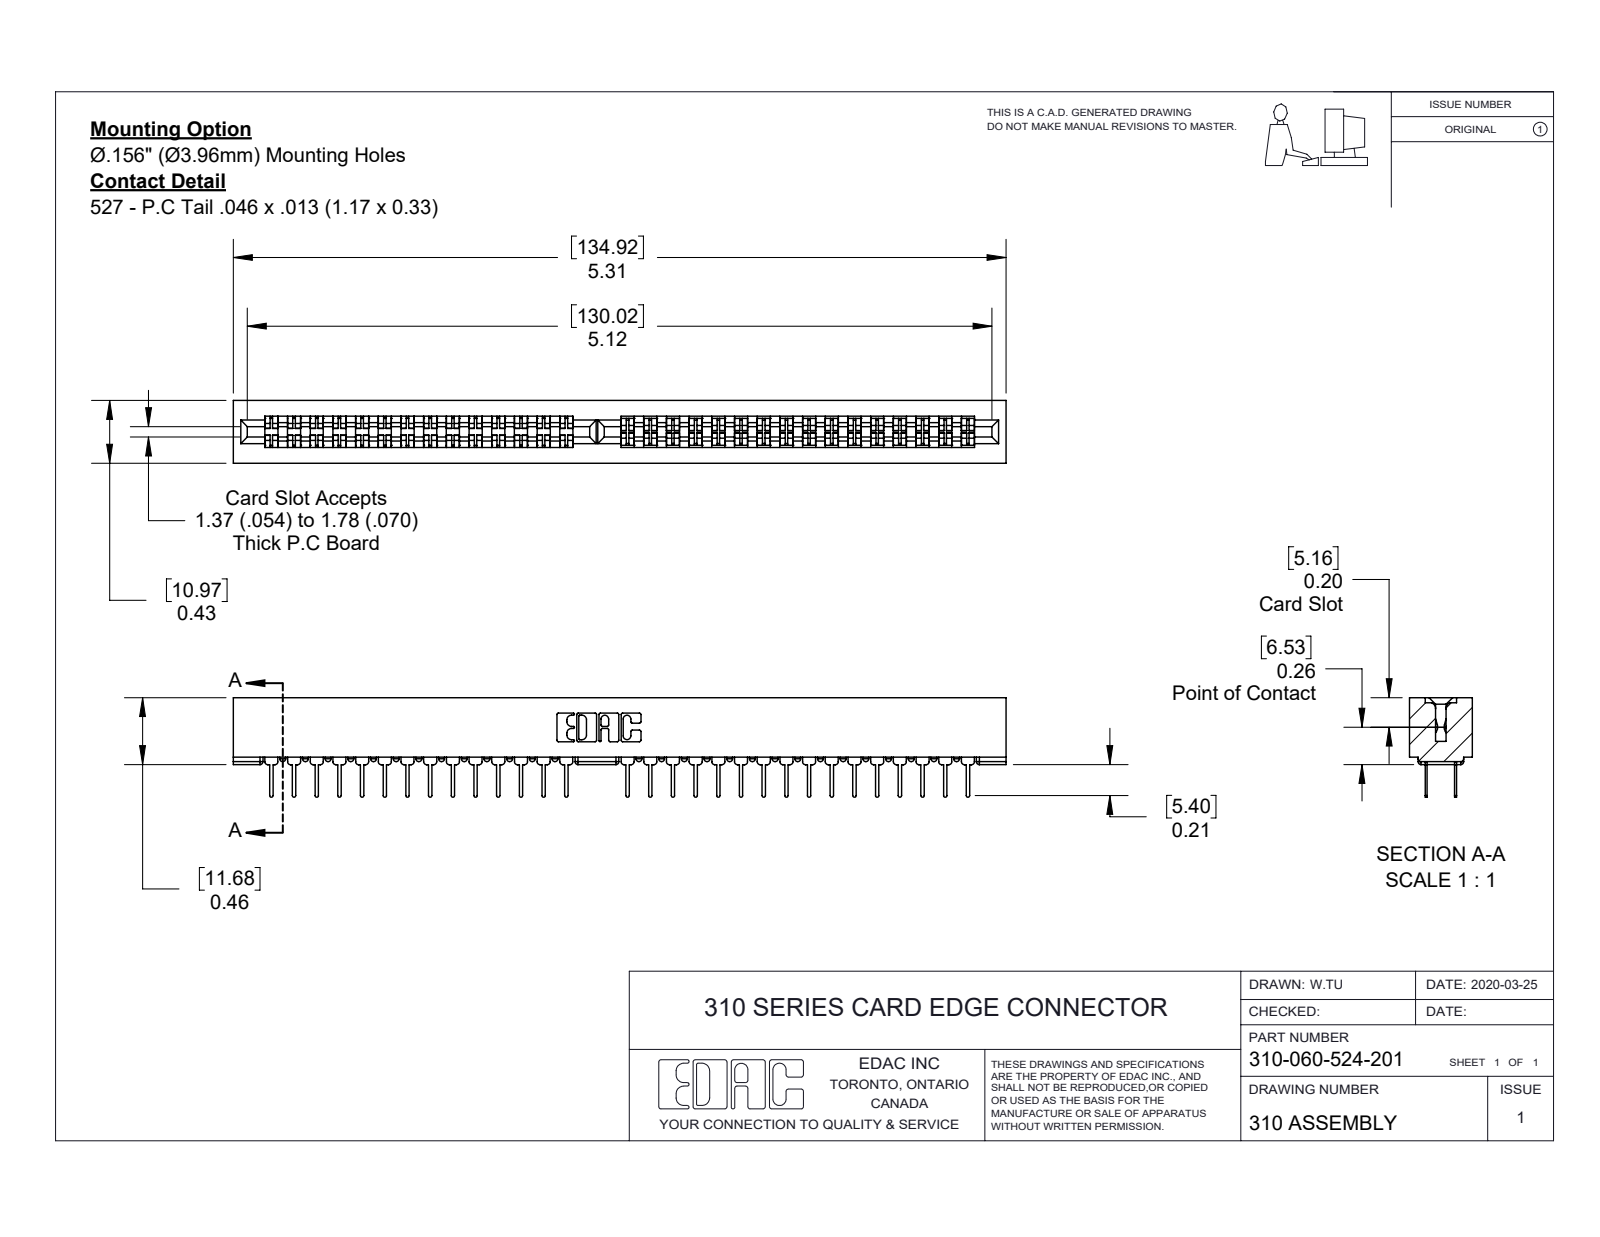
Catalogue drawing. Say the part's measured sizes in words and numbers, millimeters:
The part is named "310-060-524-201; 307-290-001_524; 310 Part_No Mounting Lugs". Its 3-D file was written by "SolidWorks 2016 (CONFIG_CONTROL_DESIGN)". It is 61 solids with 2918 faces: 1940 planar, 914 cylindrical and 64 other. Overall it measures 134.93 by 17.37 by 10.97 millimeters. Its volume is 11 991 cubic millimeters and its surface area 16 579 square millimeters. Partial cylindrical surfaces (rounded edges, fillets, slot ends): 158 of radius 0.51, 30 of radius 0.29, 22 of radius 0.25, 6 of radius 0.17, 6 of radius 0.8, 4 of radius 0.3, 4 of radius 0.64, 4 of radius 1.19. The main face-to-face distances are 2.76, 8.22, 0.33, 0.38, 4.75, 10.98, 5.46, 1.82, 3.14, 7.84.
